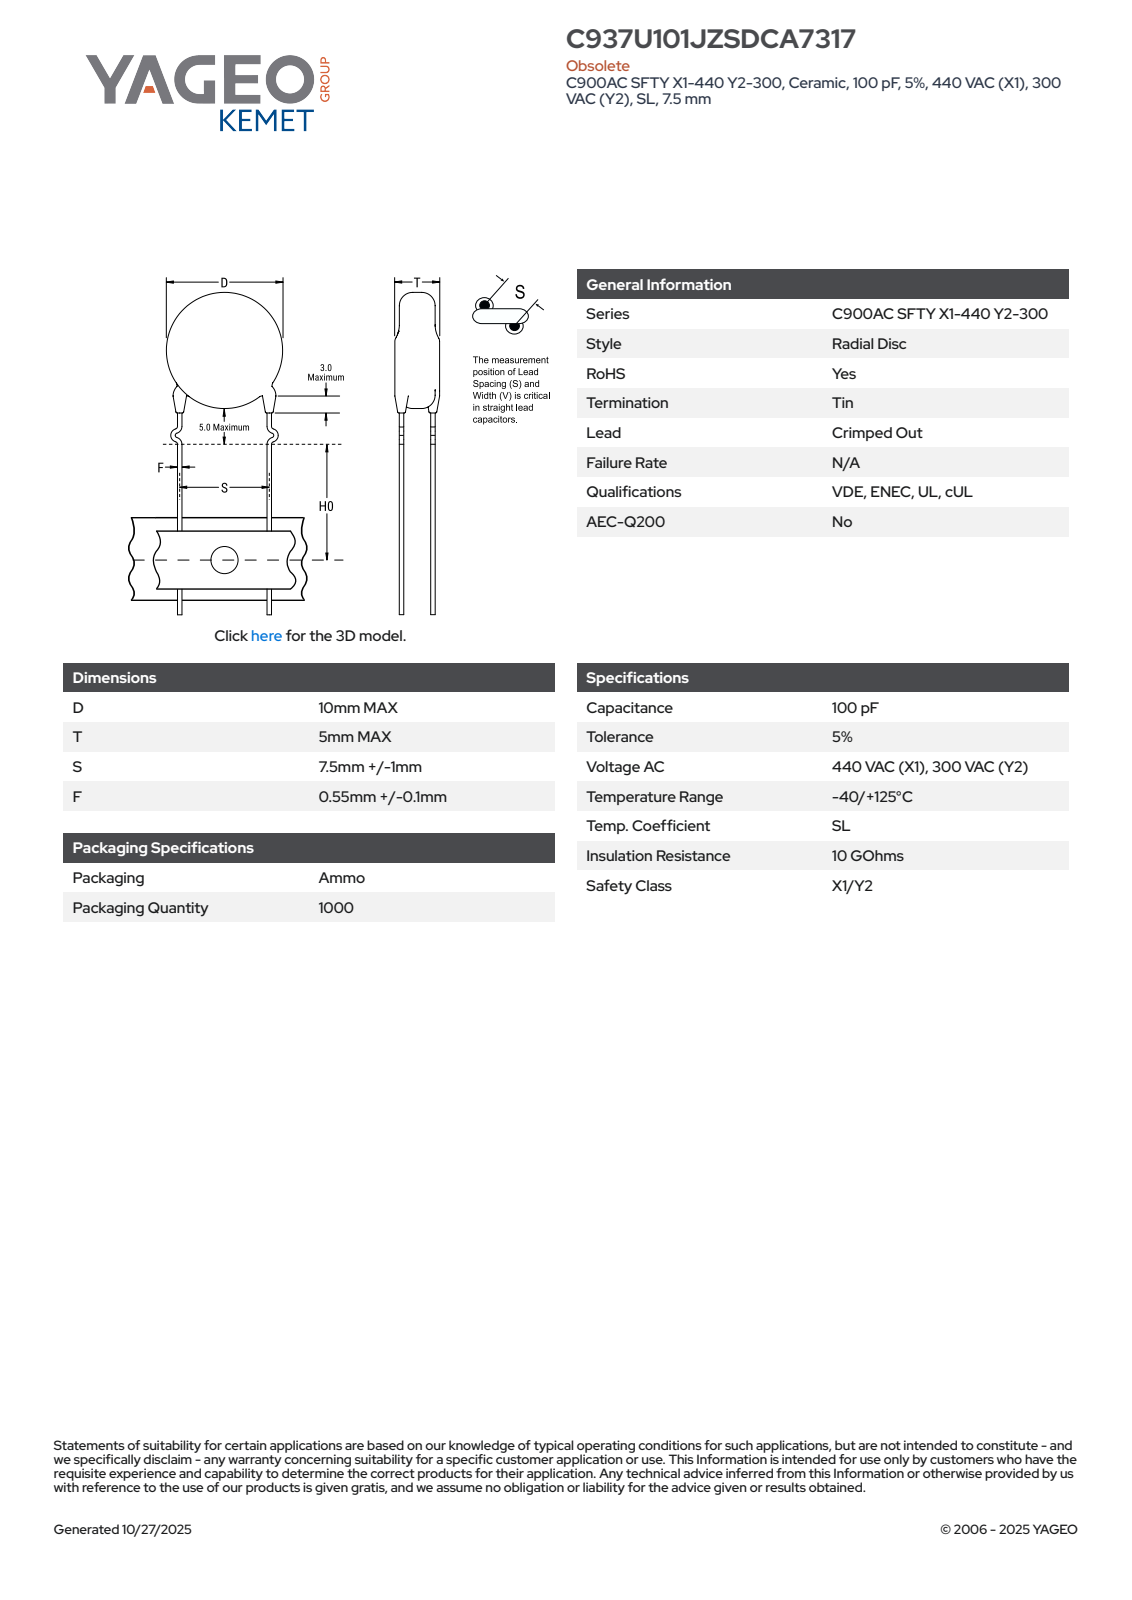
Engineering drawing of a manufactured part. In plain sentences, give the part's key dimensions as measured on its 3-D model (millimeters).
The part is named "CCD_KCOC900_D10T5S7.5LL20F0.55". Its 3-D file was written by "SolidWorks 2014 (AUTOMOTIVE_DESIGN)". It is 4 solids with 85 faces: 63 planar, 6 cylindrical and 16 other. Overall it measures 35 by 12.44 by 5 millimeters. Its volume is 401 cubic millimeters and its surface area 416 square millimeters. Round bosses or shafts: 2 of diameter 1.2, 1 of diameter 10. The main face-to-face distances are 5, 1.04, 5.53, 4.49, 0.84, 4.24, 0.38, 4.52, 3.08, 3.2.
